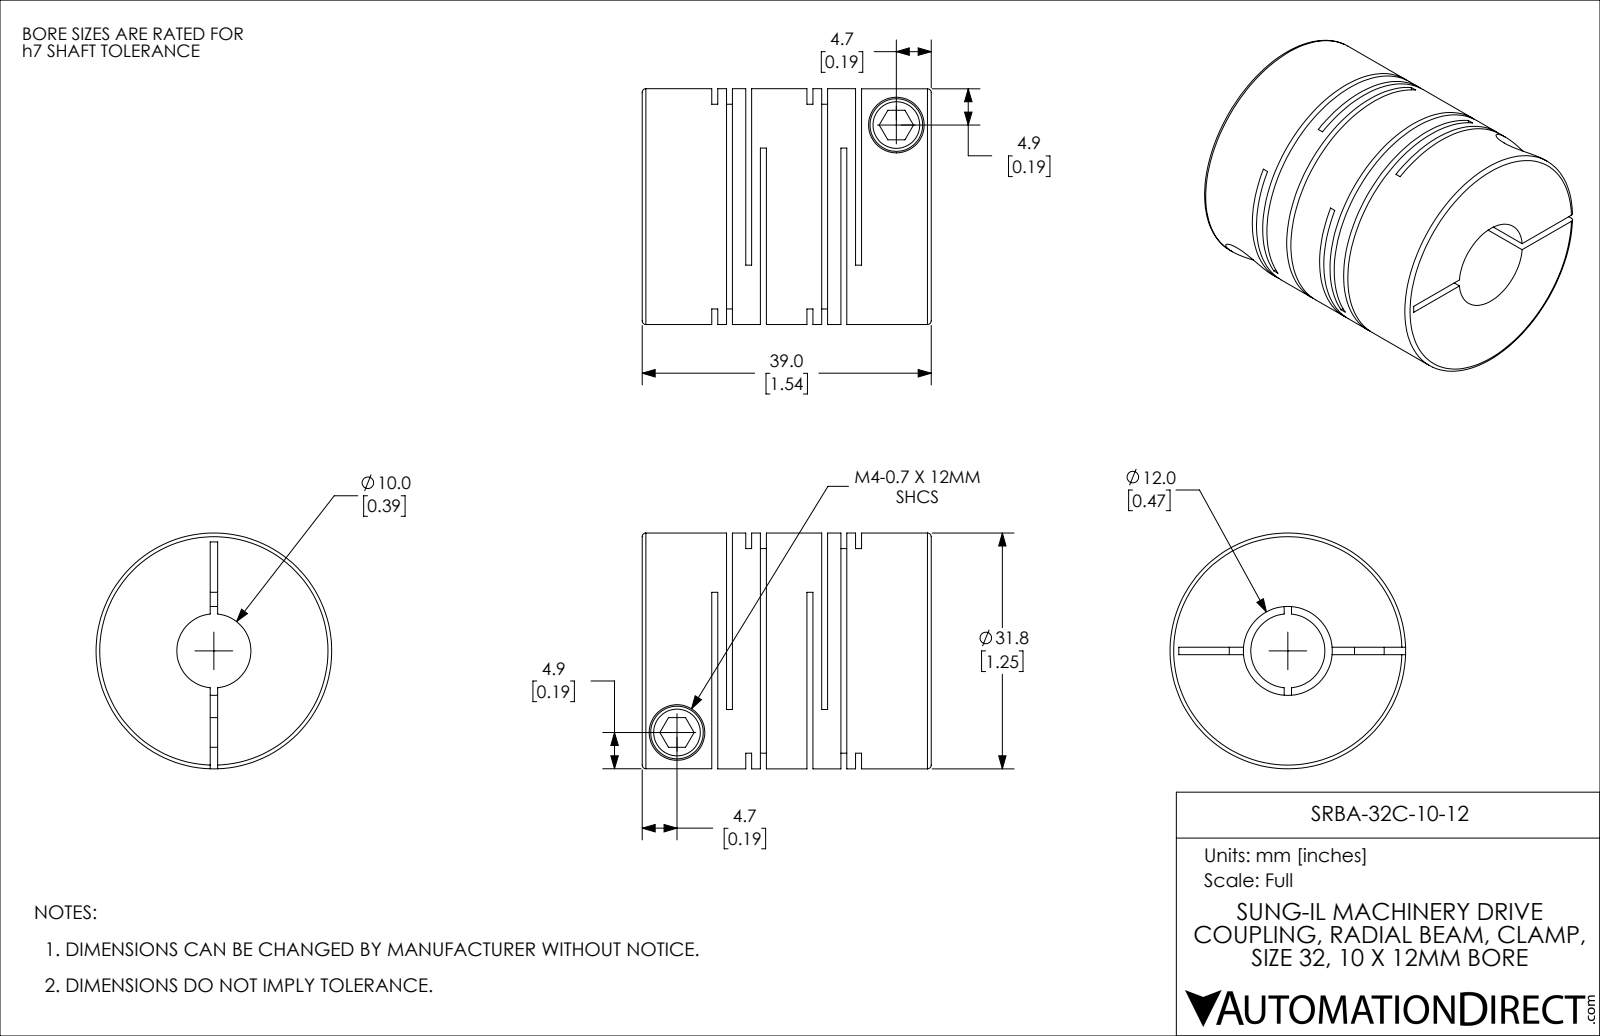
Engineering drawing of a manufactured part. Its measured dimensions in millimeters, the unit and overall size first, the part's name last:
Units: millimetres
Overall size (bounding box): 39 × 31.8 × 31.8
Round holes (diameter × count): ⌀4 ×2, ⌀7.5 ×2, ⌀10 ×1, ⌀12 ×1
Round bosses / shafts (diameter × count): ⌀7.1 ×2, ⌀31.8 ×1
Main face-to-face distances: 0.8, 1.98, 4.58, 12.84, 12.04, 1.18, 10.86, 3.78, 8.26, 2.6
Volume: 22 667 mm³ · Surface area: 15 767 mm²
Bodies: 1 solid, 114 faces (60 planar, 42 cylindrical, 12 other)
Part name (STEP PRODUCT): SRBA-32C-10-12
STEP written by: SolidWorks 2021 (CONFIG_CONTROL_DESIGN)
